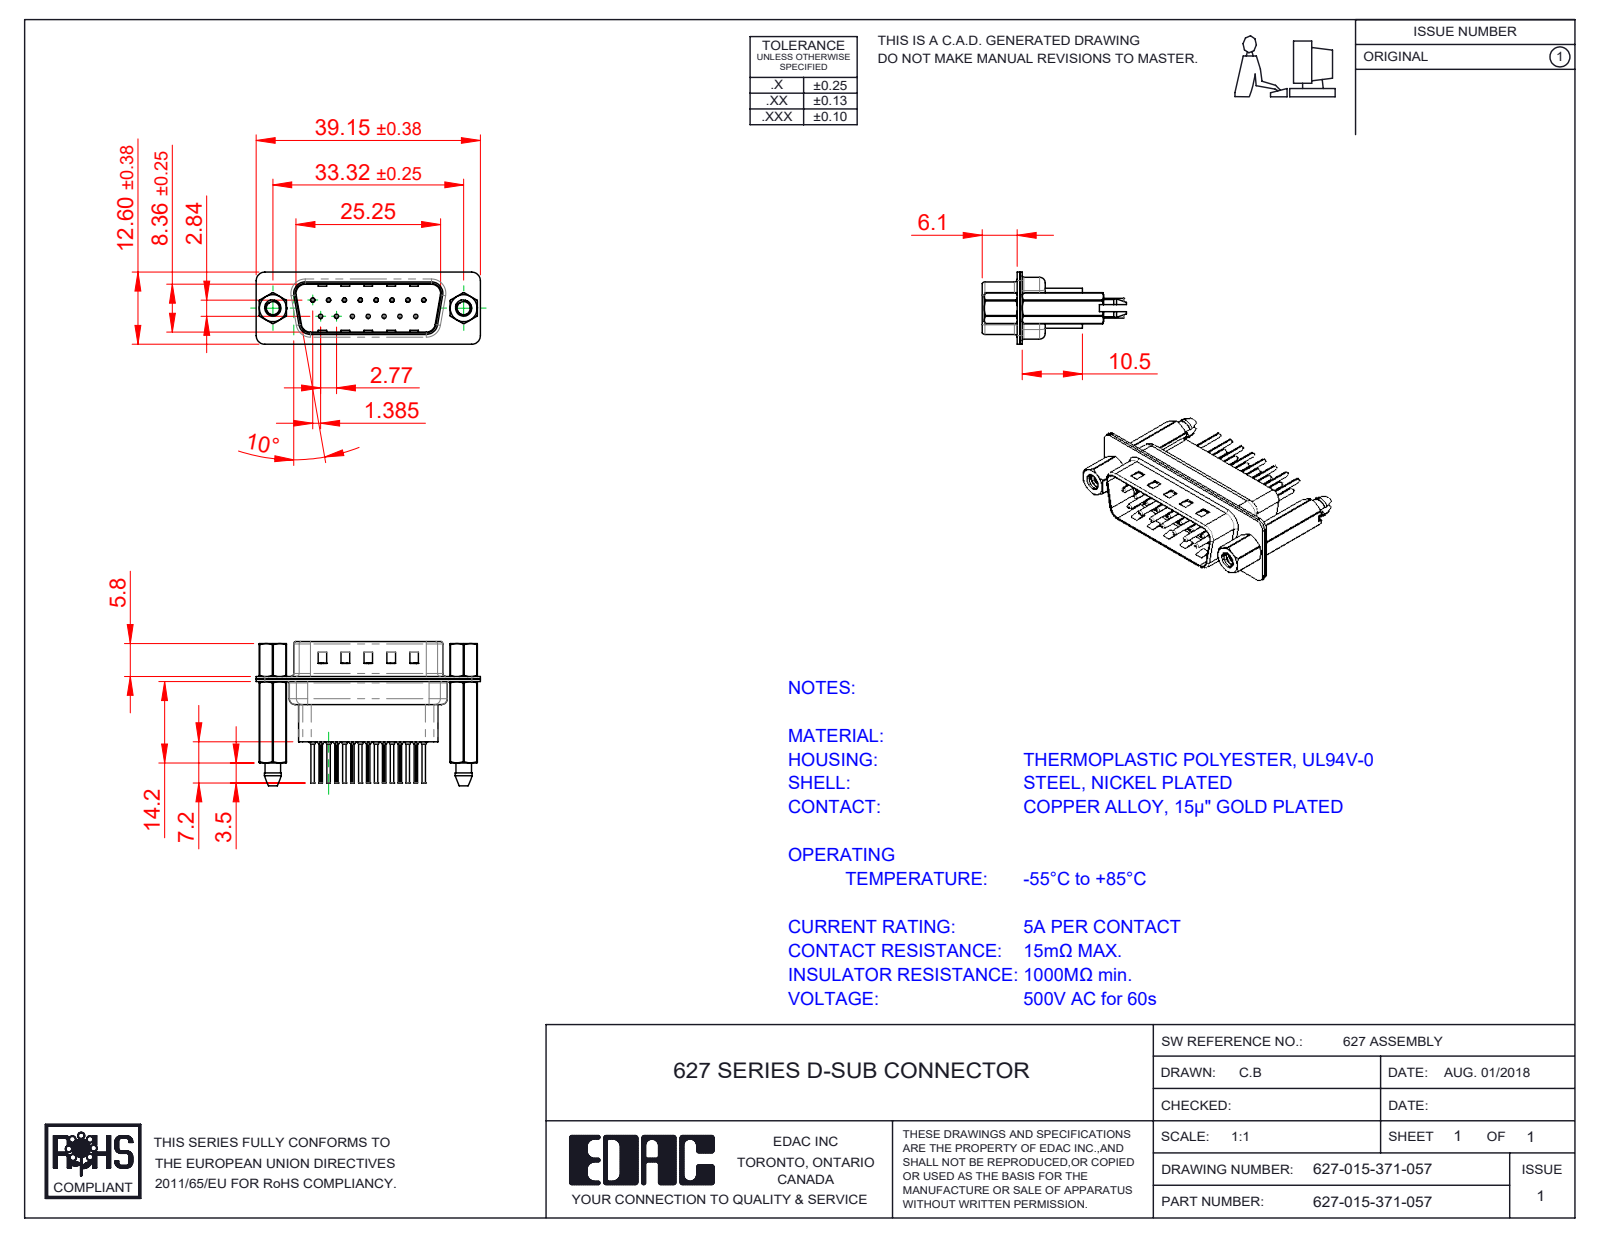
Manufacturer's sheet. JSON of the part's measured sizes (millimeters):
{"part_name": "627 Contact Row 1_61; 627 Shell Front_15 Contacts; 627 Contact Row 2_61; 627-015-371-057 (+4 more)", "step_written_by": "SolidWorks 2020 (CONFIG_CONTROL_DESIGN)", "units": "millimeters", "bodies": {"solids": 22, "faces": 2044, "planar": 553, "cylindrical": 826, "other": 665}, "overall_size": [39.15, 25.1, 12.6], "volume_mm3": 3123, "surface_area_mm2": 8000, "round_holes": [[0.2, 15], [0.35, 15], [1.1, 15], [1.6, 15], [2.26, 2], [2.29, 2], [4, 2], [4.8, 2]], "round_bosses_or_shafts": [[2, 15], [1.5, 15], [0.75, 15], [0.6, 15], [4.9, 2], [2.79, 2]], "partial_cylinders_radius": [[0.1, 30], [1.5, 18], [2, 12], [1.6, 10], [0.5, 8], [0.25, 4], [0.6, 4], [0.65, 4]], "face_to_face_distances": [0.4, 0.45, 4.76, 0.9, 0.82, 9.58, 1.5, 0.68, 7.68, 16.66], "hole_center_spacings": [3.16, 2.77, 5.54, 8.31, 11.08, 5.03, 5.04, 7.48]}
